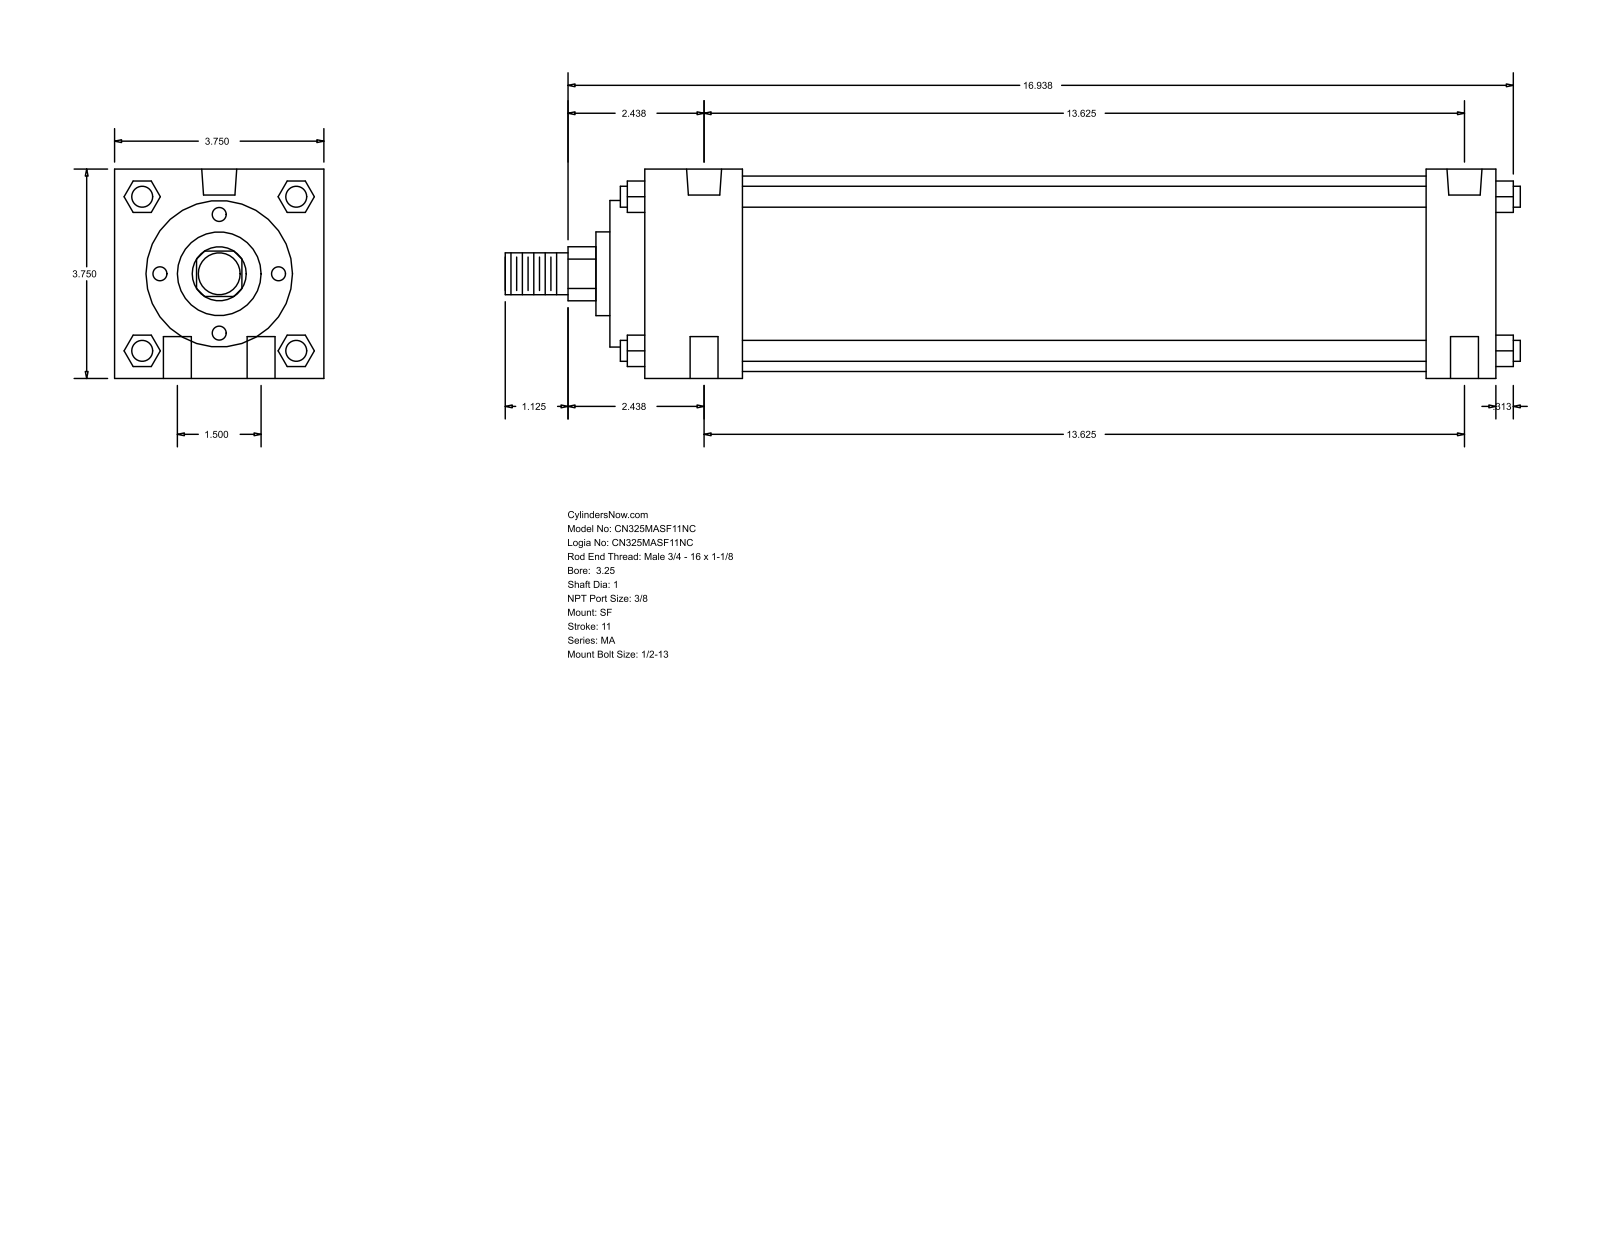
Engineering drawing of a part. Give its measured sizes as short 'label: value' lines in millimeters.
name: MA_SF__0325_1
written by: GSSL Pune (CONFIG_CONTROL_DESIGN)
unit: mm
bodies: 0 solids, 126 faces (95 planar, 31 cylindrical, 0 other)
size: 461.96 × 95.25 × 95.25
holes: 4× ⌀12.7, 2× ⌀11.11, 2× ⌀15.93
bosses: 4× ⌀9.53, 1× ⌀88.9, 1× ⌀66.67, 1× ⌀38.1, 1× ⌀25.4, 1× ⌀19.05
rounds: 1× R12.29
face distances: 95.24, 387.35, 403.22, 355.6, 31.75, 44.46, 311.14, 342.89, 15.87, 60.33
hole spacings: 19.05, 346.6, 346.08, 38.1, 348.17, 336.56
